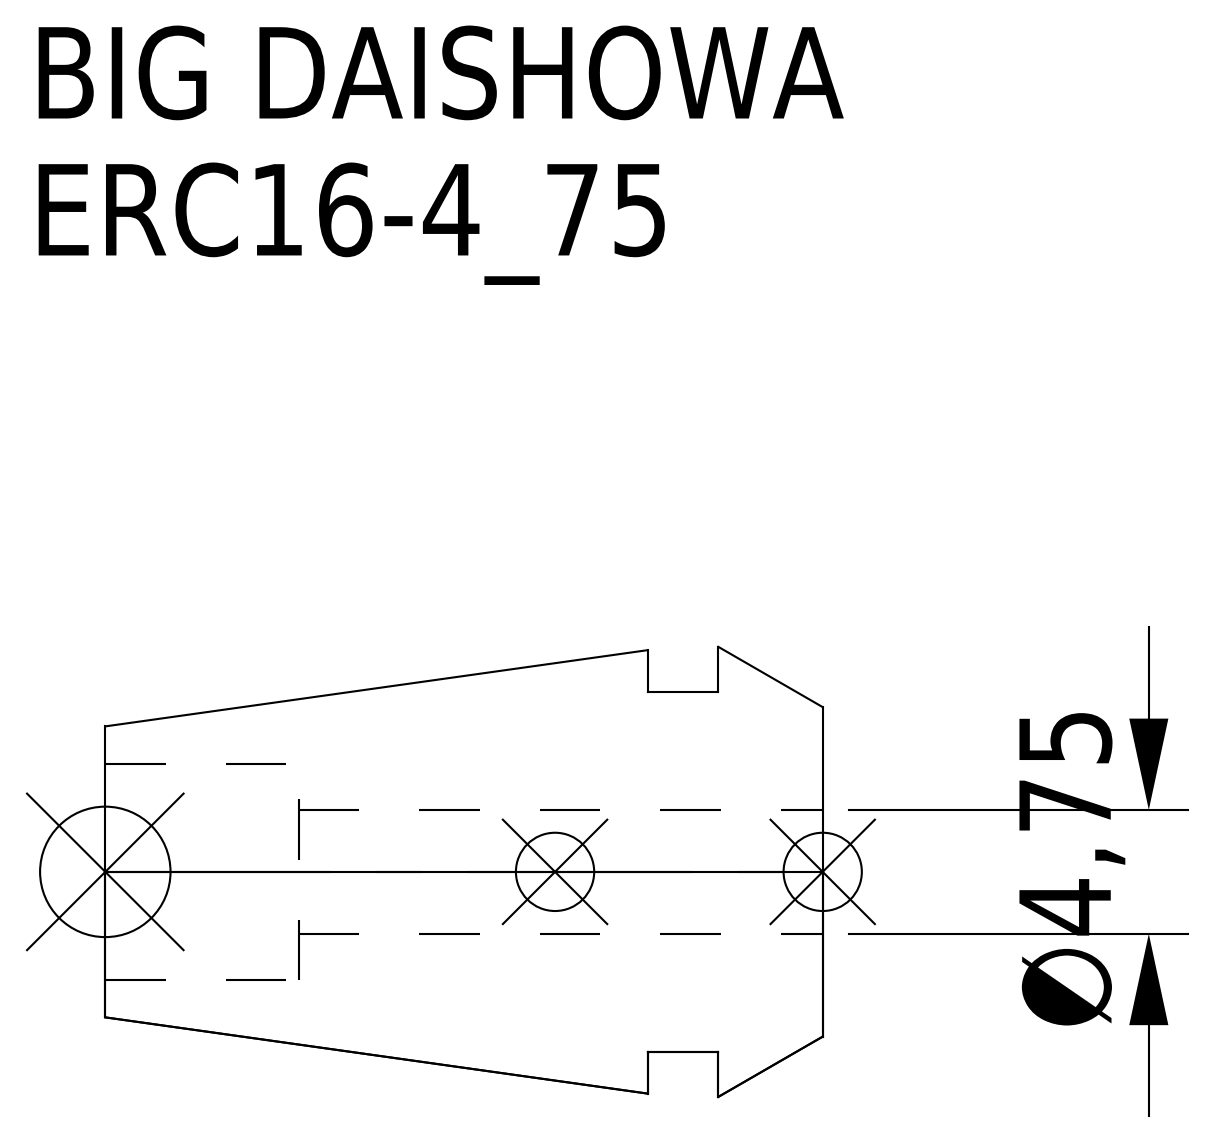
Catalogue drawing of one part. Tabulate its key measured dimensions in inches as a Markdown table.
| quantity | value |
| --- | --- |
| part name | ERC16-4_75 |
| STEP written by | CREO PARAMETRIC BY PTC INC, 2016380 (AUTOMOTIVE_DESIGN) |
| units | inches |
| bodies | 1 solid, 15 faces (5 planar, 6 cylindrical, 4 other) |
| overall size | 1.083 × 0.679 × 0.679 |
| volume | 0.222 in³ |
| surface area | 3.263 in² |
| round holes (diameter × count) | 0.187 × 1, 0.327 × 1 |
| round bosses / shafts (diameter × count) | 0.543 × 1 |
| main face-to-face distances | 0.157, 0.264, 0.106, 1.083, 0.925, 0.819, 0.791, 0.633, 0.527, 0.292 |
